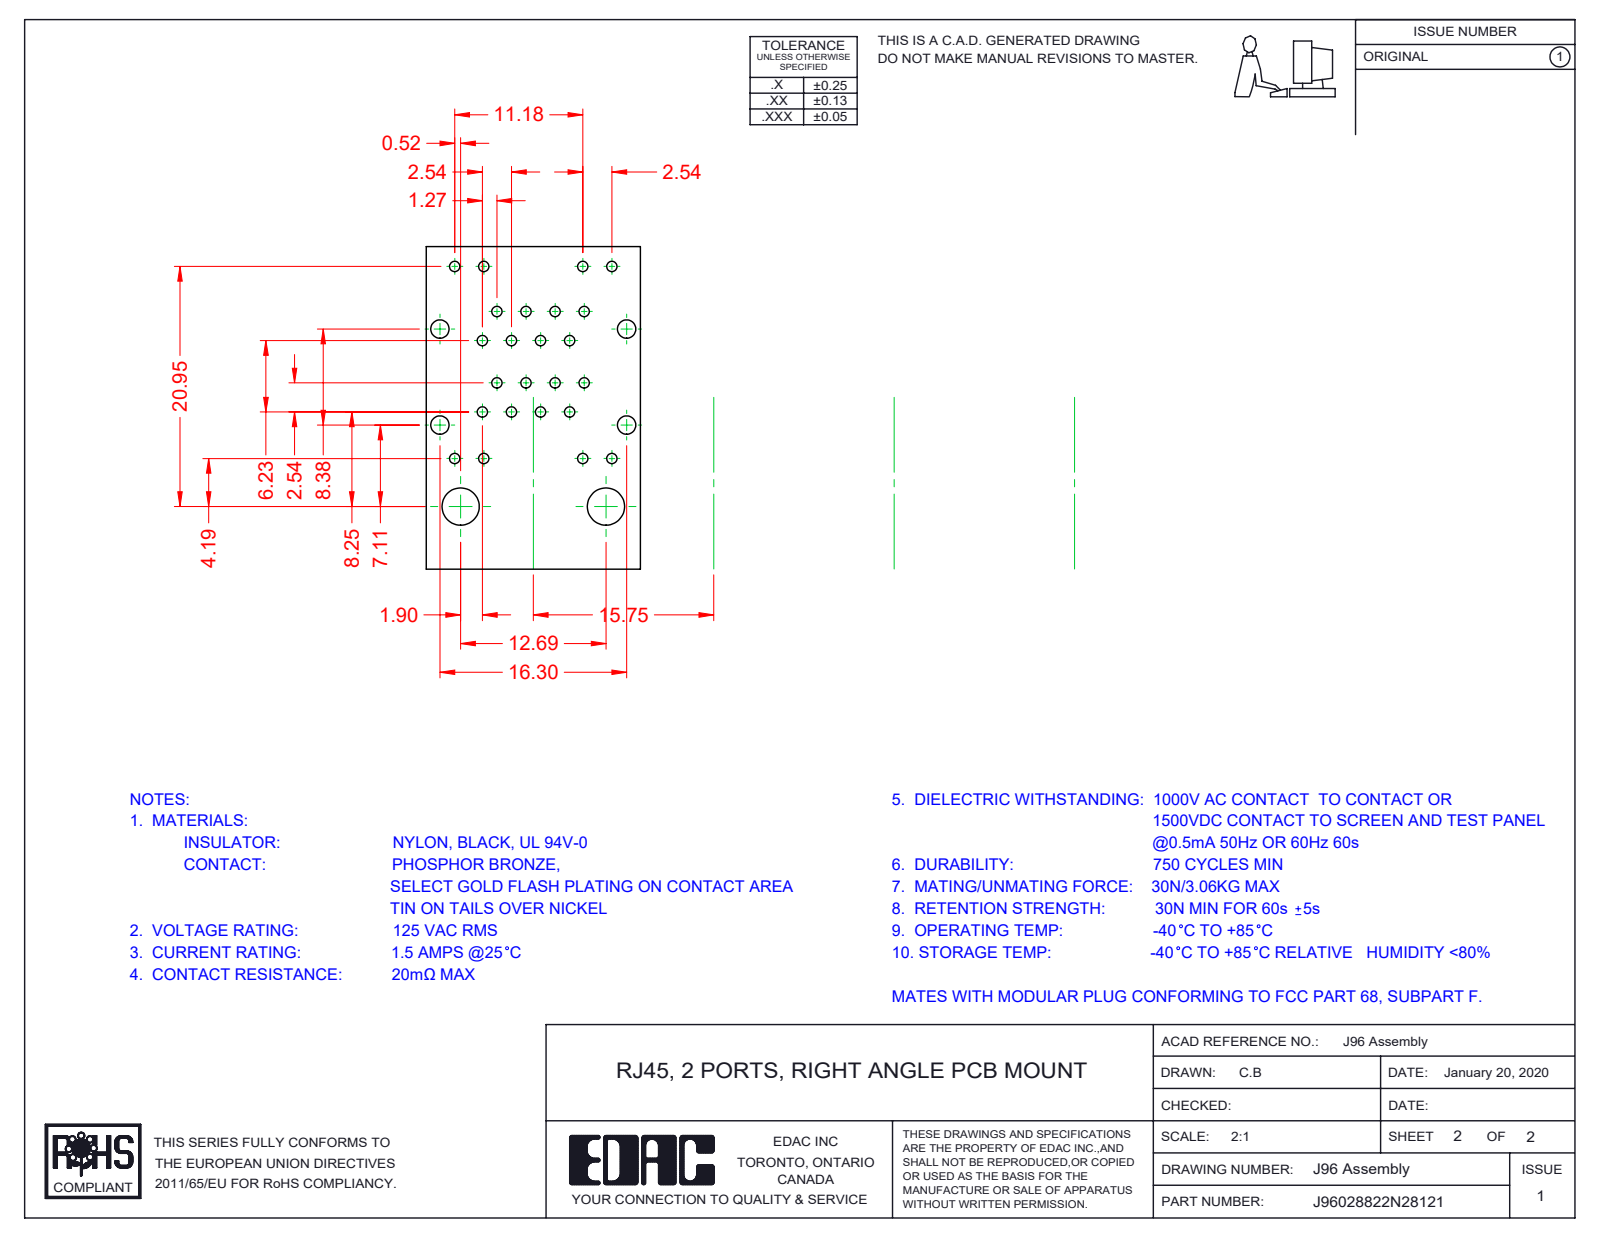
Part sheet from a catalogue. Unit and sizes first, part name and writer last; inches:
Units: inches
Overall size (bounding box): 1.165 × 1.129 × 0.661
Partial cylindrical surfaces — rounded edges, fillets, slot ends (radius × count): R0.01 ×48, R0.006 ×32, R0.014 ×24, R0.02 ×16, R0.039 ×16, R0.008 ×13, R0.028 ×9, R0.079 ×5
Main face-to-face distances: 0.642, 0.634, 0.069, 0.65, 0.581, 0.061, 0.573, 0.021, 0.058, 0.441
Volume: 0.418 in³ · Surface area: 29.62 in²
Bodies: 27 solids, 2386 faces (1849 planar, 431 cylindrical, 106 other)
Part name (STEP PRODUCT): 96 Contact Lock Lower; 96 LED RH Lower_8-Red-Yellow; J96028822N28121; 96 LED RH Upper_8-Red-Yellow (+8 more)
STEP written by: SolidWorks 2016 (CONFIG_CONTROL_DESIGN)
